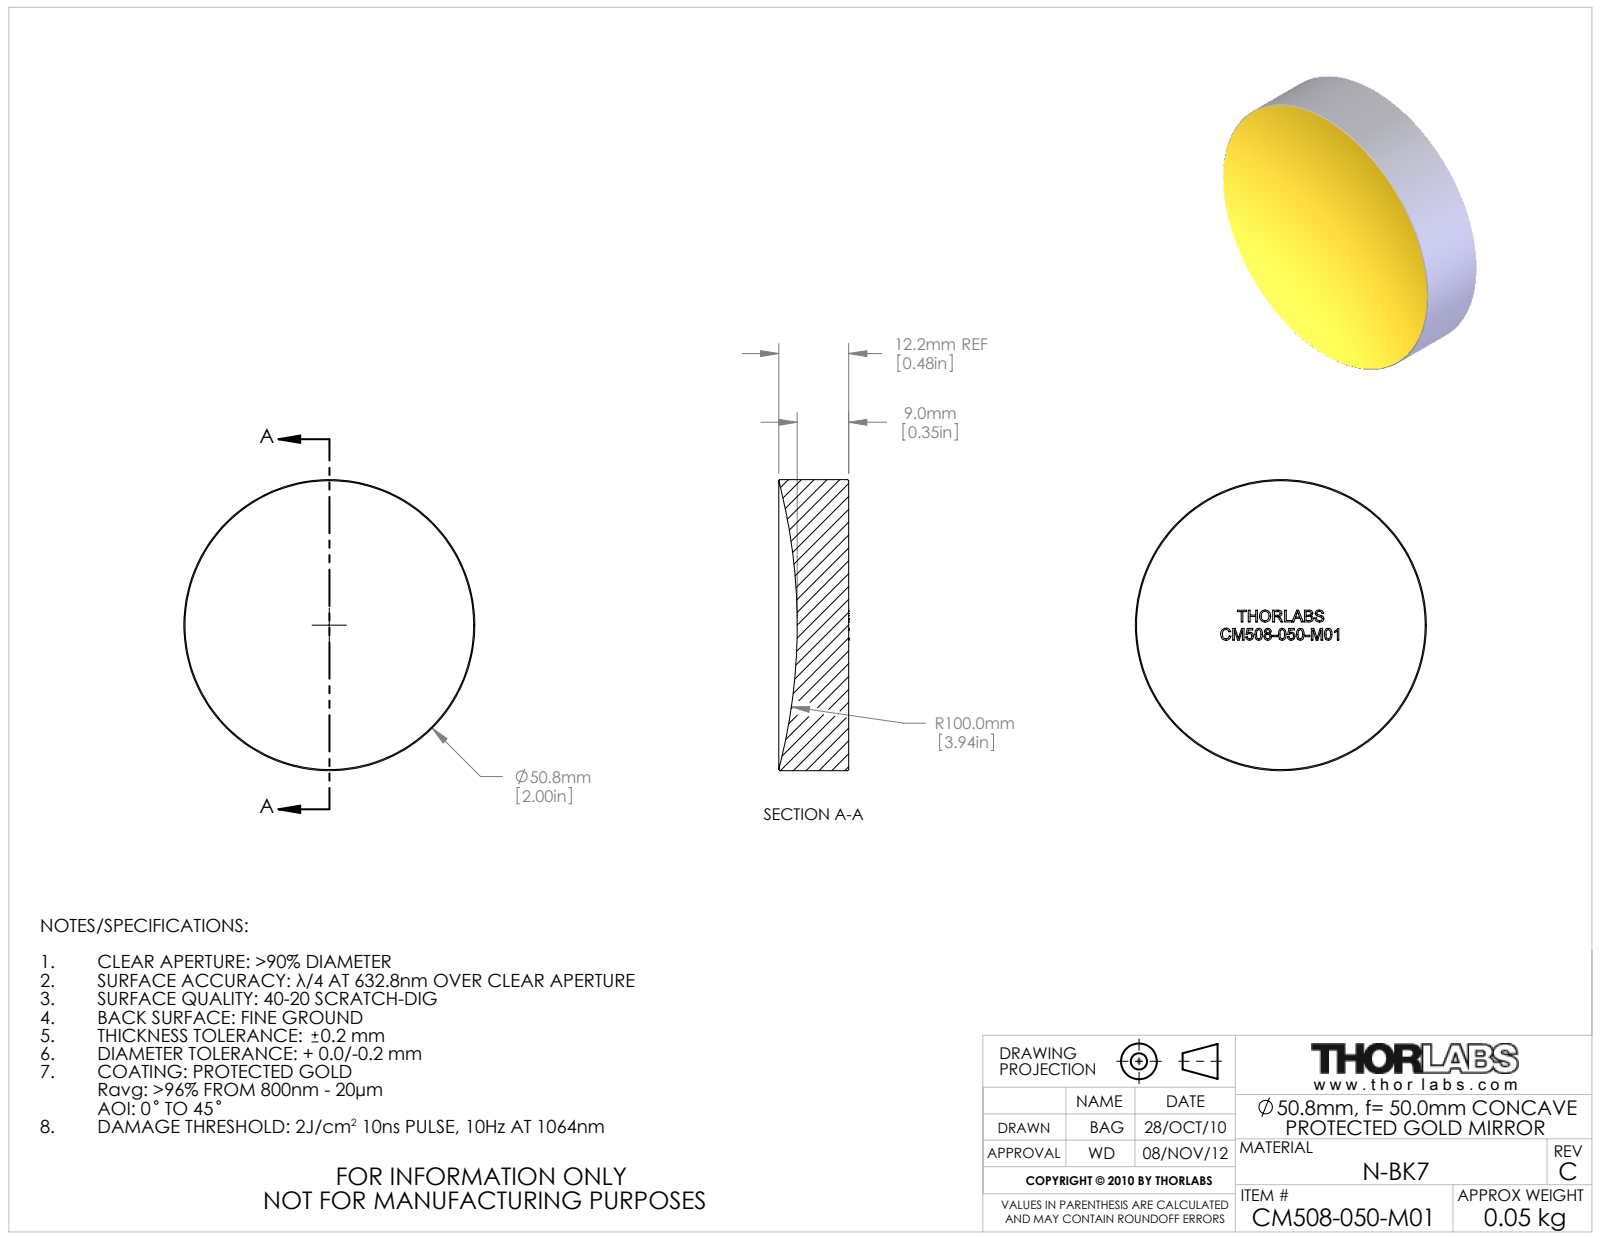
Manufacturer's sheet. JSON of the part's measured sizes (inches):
{"part_name": "17586-E0W", "step_written_by": "SolidWorks 2009 (AUTOMOTIVE_DESIGN)", "units": "inches", "bodies": {"solids": 1, "faces": 285, "planar": 147, "cylindrical": 2, "other": 136}, "overall_size": [2, 2, 0.481], "volume_in3": 1.314, "surface_area_in2": 9.306, "round_bosses_or_shafts": [[2, 1]], "face_to_face_distances": [0.081, 0.125, 0.1, 0.549, 0.124, 0.218, 0.249, 0.038, 0.449, 0.541]}
